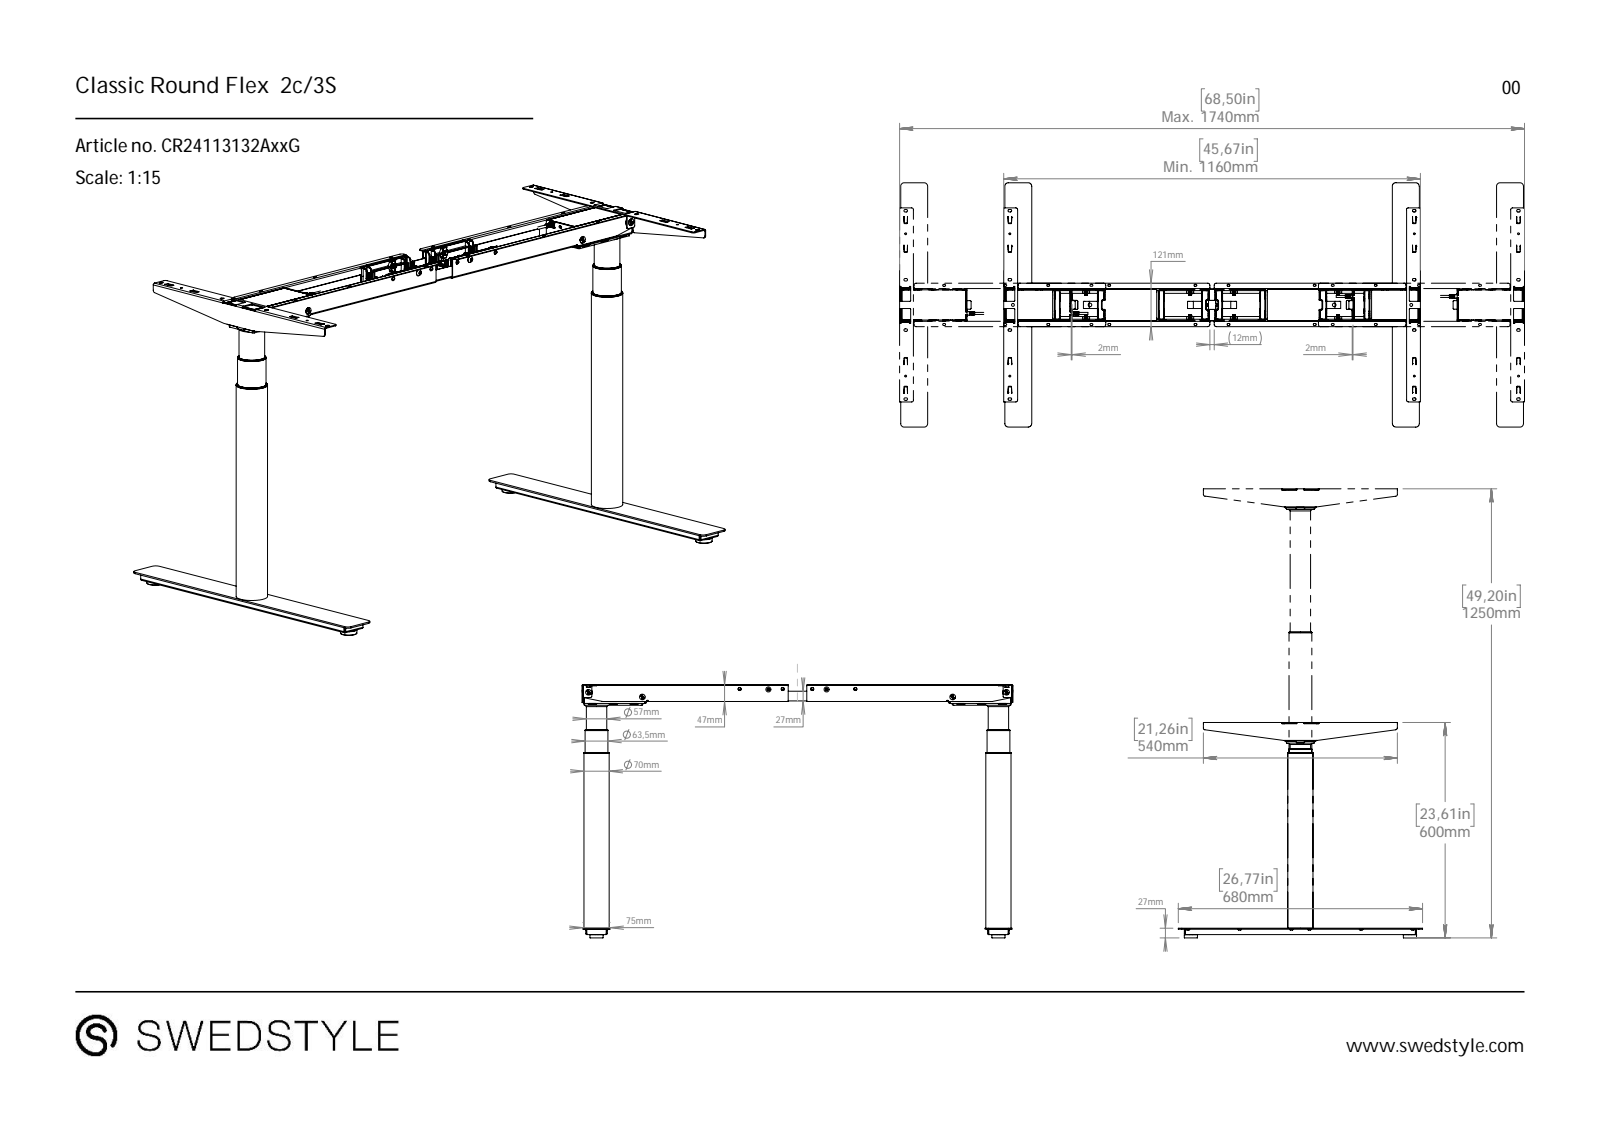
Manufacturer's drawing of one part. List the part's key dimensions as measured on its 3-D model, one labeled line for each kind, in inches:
Part name (STEP PRODUCT): CR24113132AxxG_Classic Round Flex 2c_3S, Fl116
STEP written by: SolidWorks 2021 (CONFIG_CONTROL_DESIGN)
Units: inches
Bodies: 0 solids, 2051 faces (1001 planar, 621 cylindrical, 429 other)
Overall size (bounding box): 47.244 × 27.756 × 26.772
Round holes (diameter × count): ⌀0.591 ×8, ⌀0.315 ×4, ⌀0.236 ×2, ⌀0.339 ×2, ⌀0.394 ×2
Round bosses / shafts (diameter × count): ⌀2.756 ×2, ⌀2.5 ×2, ⌀2.244 ×2, ⌀0.613 ×2, ⌀0.335 ×2, ⌀0.299 ×2, ⌀0.217 ×2
Partial cylindrical surfaces — rounded edges, fillets, slot ends (radius × count): R0.02 ×107, R0.118 ×61, R0.098 ×60, R0.039 ×36, R0.138 ×24, R0.108 ×16, R0.059 ×10, R0.079 ×10
Main face-to-face distances: 0.059, 0.118, 0.079, 24.957, 25.016, 24.898, 0.02, 3.642, 26.61, 1.654
Hole centre spacings: 0.866, 1.339, 1.594, 3.761, 4.616, 8.236, 9.1, 10.415
